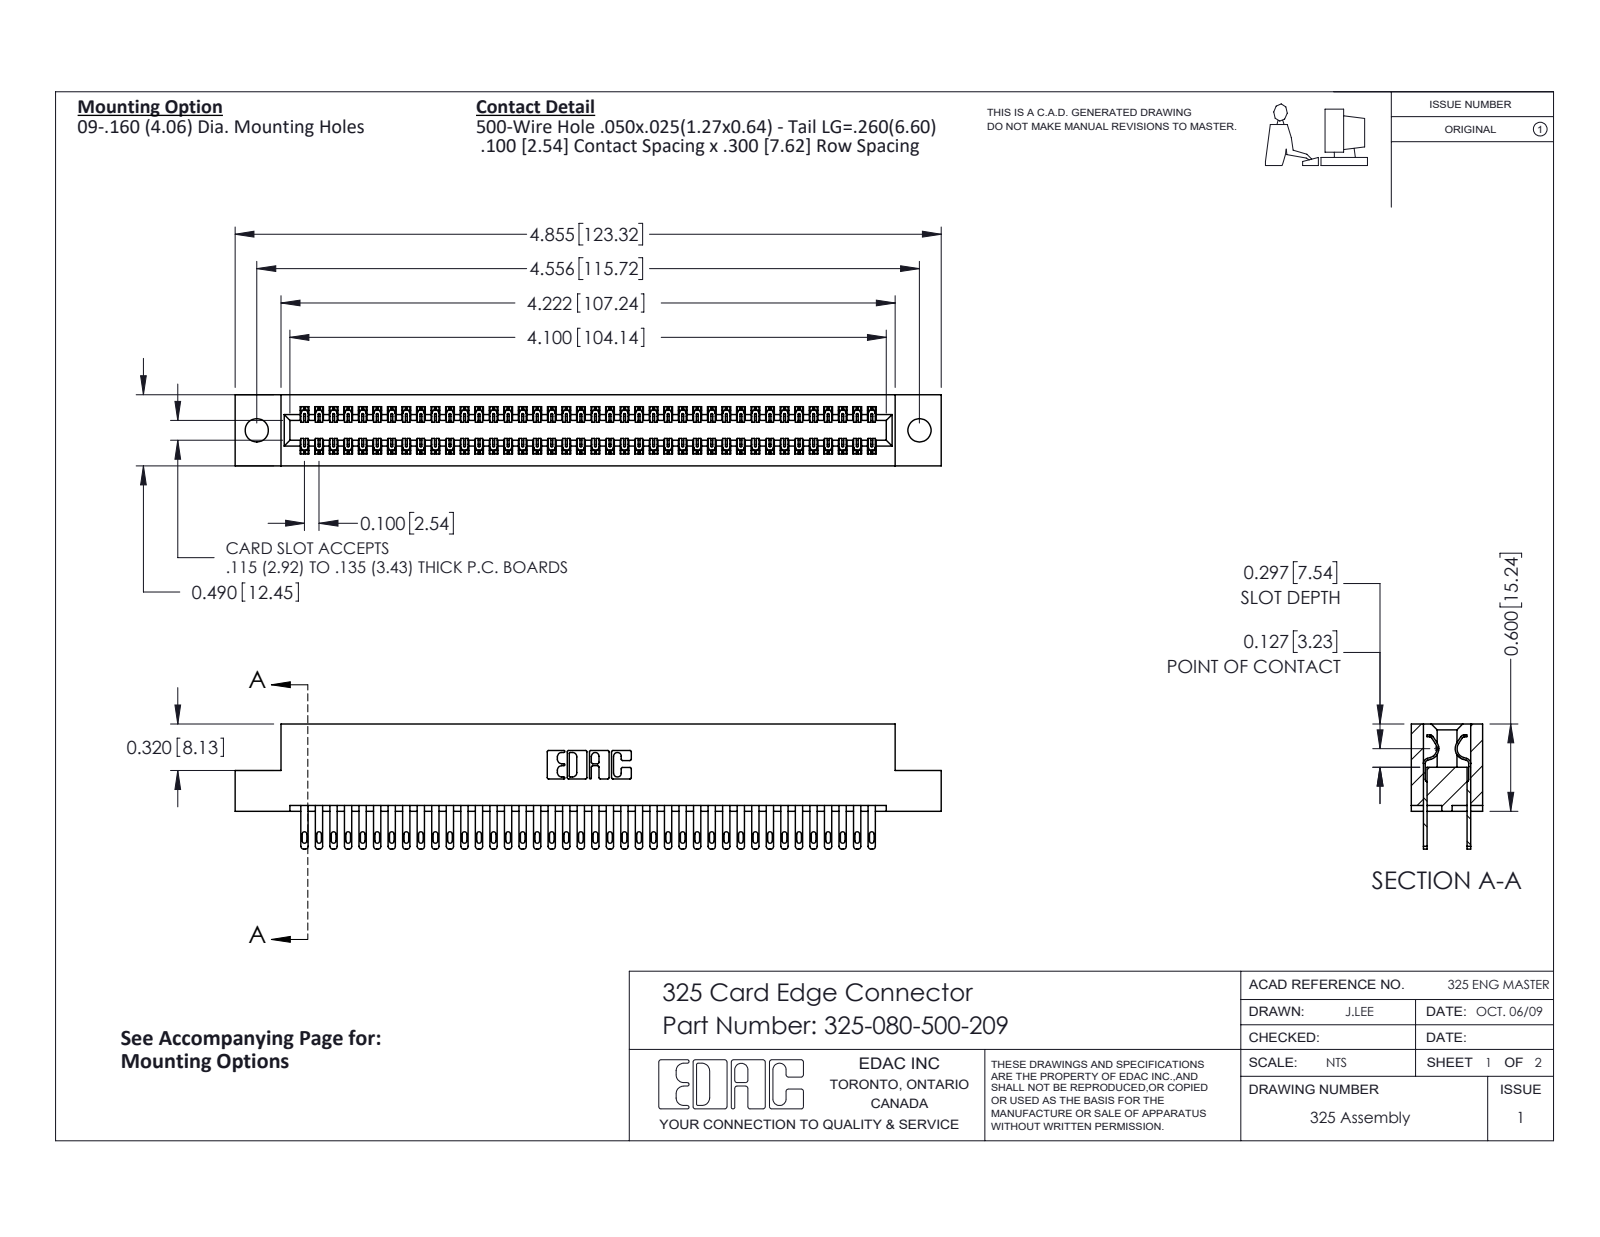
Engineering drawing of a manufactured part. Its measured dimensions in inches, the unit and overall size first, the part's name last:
Units: inches
Overall size (bounding box): 4.855 × 0.86 × 0.49
Round holes (diameter × count): ⌀0.16 ×2
Partial cylindrical surfaces — rounded edges, fillets, slot ends (radius × count): R0.006 ×120, R0.016 ×80, R0.02 ×80, R0.01 ×22, R0.007 ×6, R0.031 ×6, R0.026 ×3, R0.014 ×2
Main face-to-face distances: 0.083, 0.407, 0.3, 0.107, 0.383, 0.025, 0.49, 0.325, 0.275, 0.56
Hole centre spacings: 4.556
Volume: 0.971 in³ · Surface area: 30.96 in²
Bodies: 81 solids, 3954 faces (2470 planar, 1484 cylindrical, 0 other)
Part name (STEP PRODUCT): 325-080-500-209; 325 Part_.160 TH; 325-292-001_325-293-100
STEP written by: SolidWorks 2016 (CONFIG_CONTROL_DESIGN)
